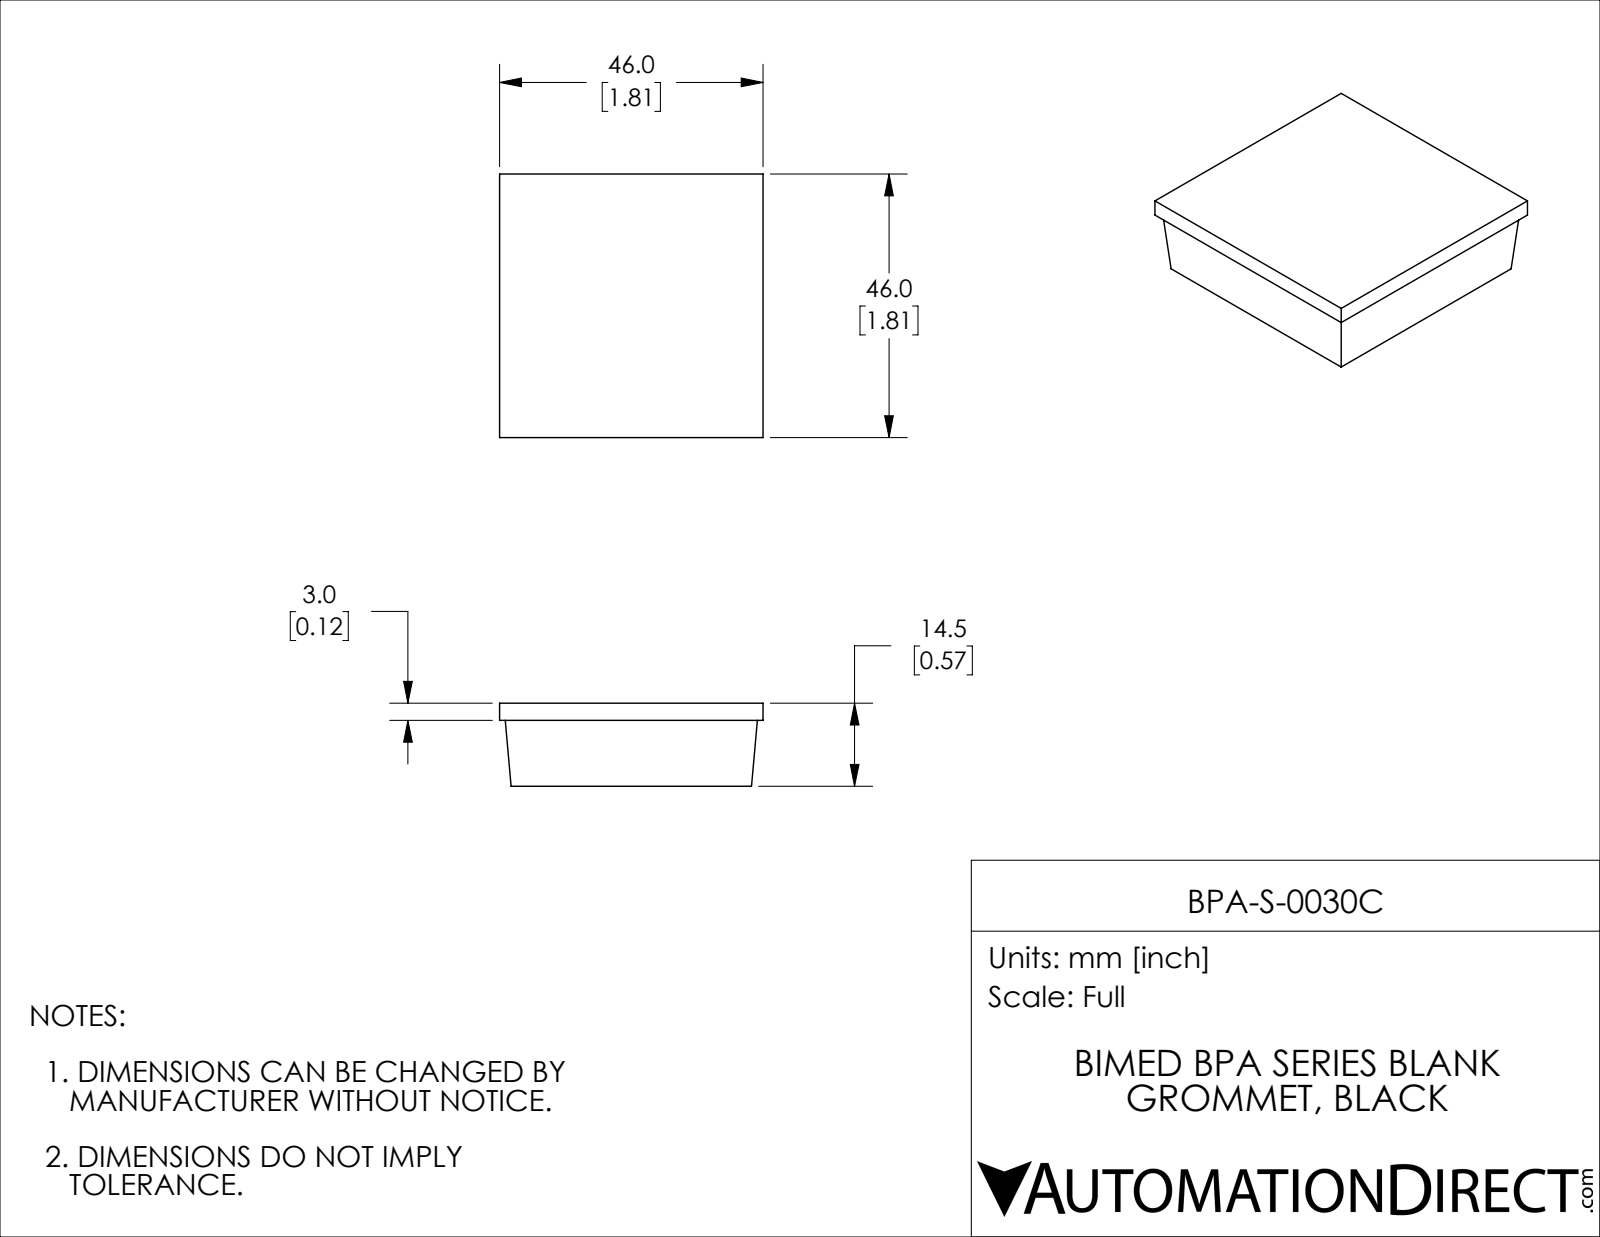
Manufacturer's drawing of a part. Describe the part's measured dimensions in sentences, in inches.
The part is named "BPA-S-0030C". Its 3-D file was written by "SolidWorks 2021 (CONFIG_CONTROL_DESIGN)". It is 1 solid with 11 faces: 11 planar, 0 cylindrical and 0 other. Overall it measures 1.811 by 1.811 by 0.571 inches. Its volume is 1.685 cubic inches and its surface area 10.22 square inches. The main face-to-face distances are 0.571, 1.811, 0.453, 0.118.
